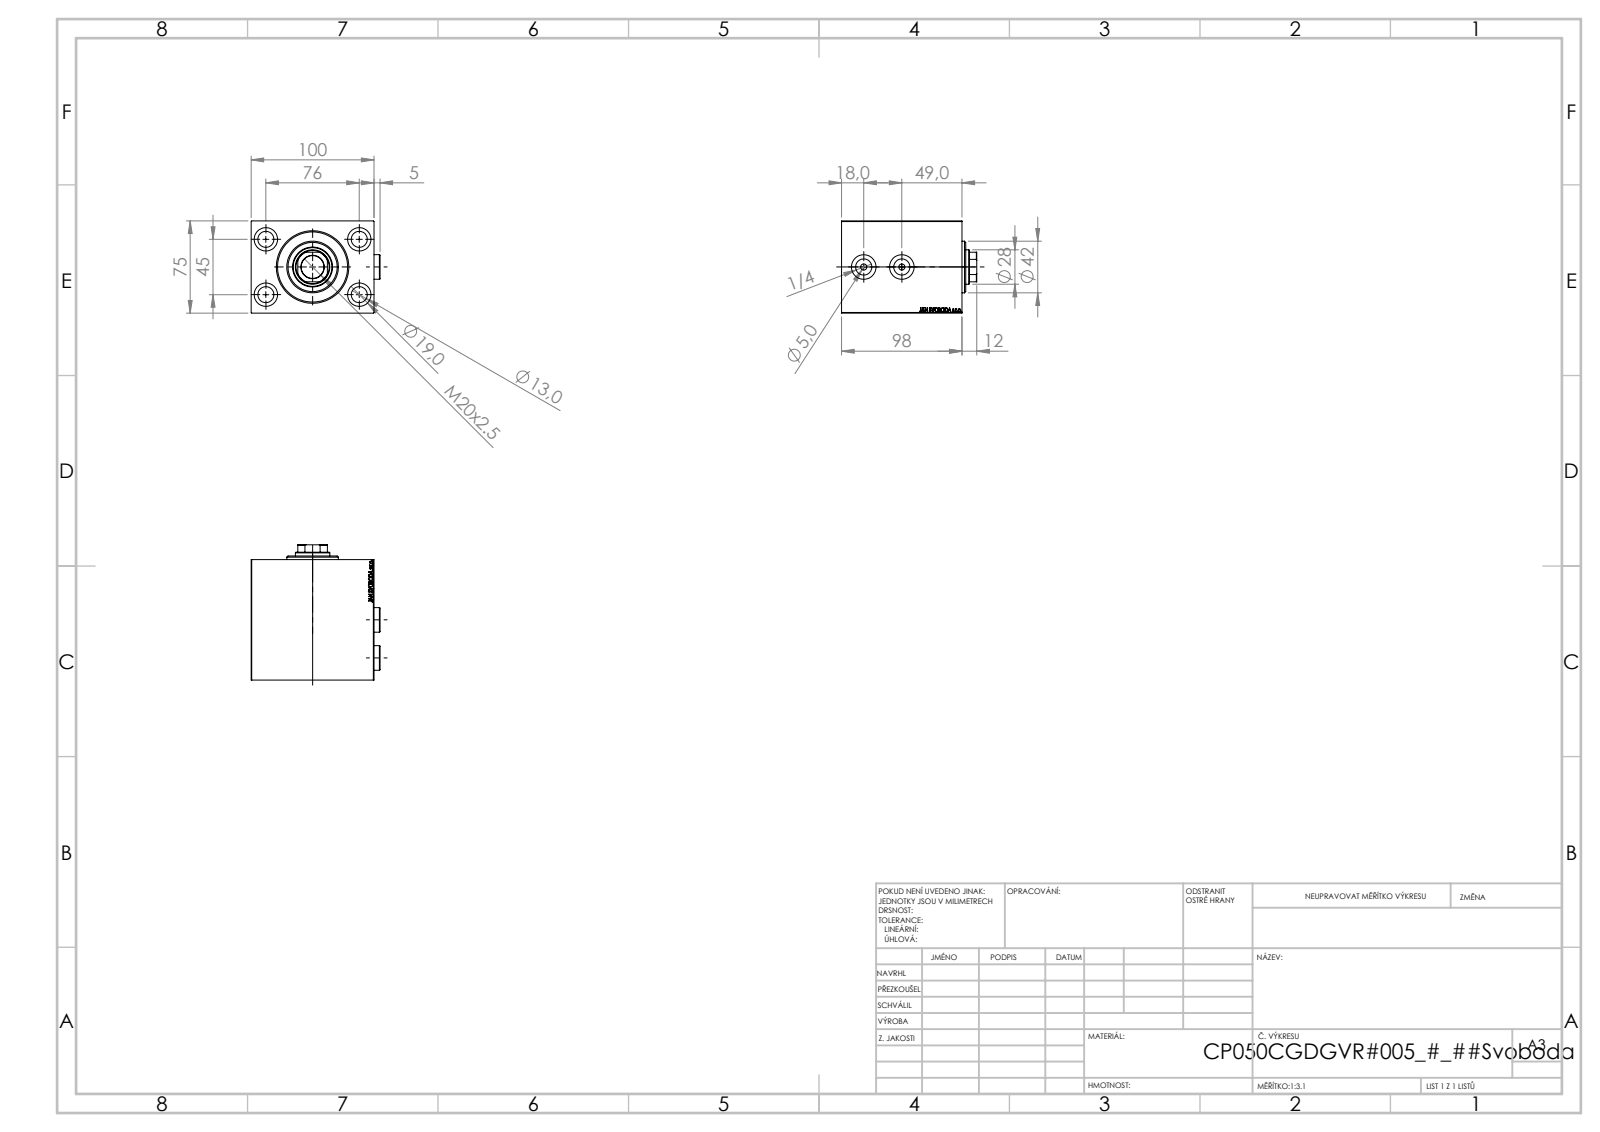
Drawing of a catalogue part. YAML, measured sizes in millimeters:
part_name: "V450CP_VC_B; V450CP_C; PLUG; V450CP_B_VCP"
step_written_by: "SolidWorks 2019 (CONFIG_CONTROL_DESIGN)"
units: millimeters
bodies: {solids: 5, faces: 943, planar: 449, cylindrical: 92, other: 402}
overall_size: [110, 104.9, 75]
volume: 655245
surface_area: 117753
round_holes:
  - {diameter: 13, count: 4}
  - {diameter: 19, count: 4}
  - {diameter: 4, count: 2}
  - {diameter: 5, count: 2}
  - {diameter: 9.73, count: 2}
  - {diameter: 13.16, count: 2}
  - {diameter: 15, count: 2}
  - {diameter: 20, count: 2}
  - {diameter: 18.5, count: 1}
  - {diameter: 28, count: 1}
  - {diameter: 31.5, count: 1}
  - {diameter: 32.5, count: 1}
round_bosses_or_shafts:
  - {diameter: 42, count: 1}
partial_cylinders:
  - {radius: 13.5, count: 1}
face_to_face_distances: [75, 100, 98, 49, 14, 84, 5, 44, 35, 13]
hole_center_spacings: [44.16, 45, 76, 88.32, 31, 42.55]
